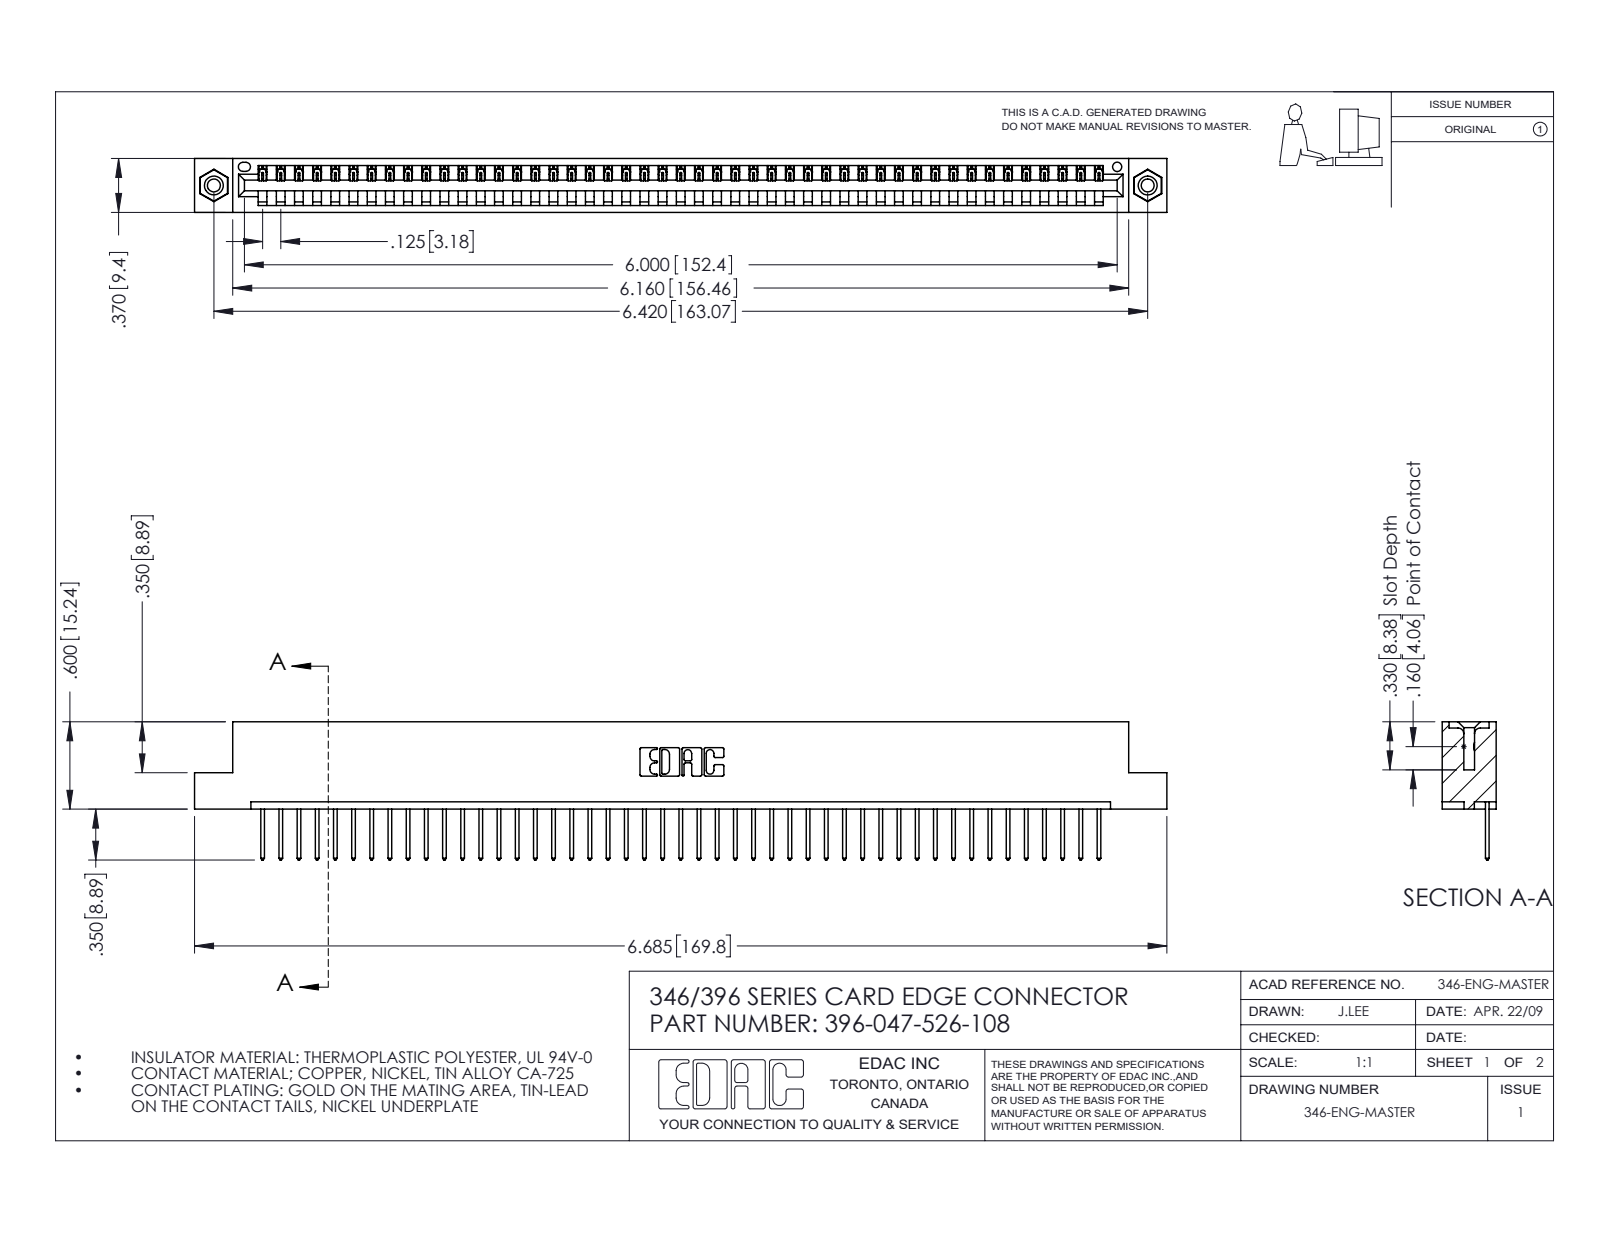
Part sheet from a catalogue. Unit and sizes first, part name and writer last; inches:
Units: inches
Overall size (bounding box): 6.685 × 0.95 × 0.37
Round holes (diameter × count): ⌀0.089 ×2, ⌀0.125 ×2, ⌀0.156 ×2, ⌀0.064 ×1
Round bosses / shafts (diameter × count): ⌀0.155 ×2
Partial cylindrical surfaces — rounded edges, fillets, slot ends (radius × count): R0.006 ×94, R0.01 ×94, R0.01 ×22, R0.007 ×6, R0.031 ×6, R0.026 ×3, R0.031 ×2, R0.04 ×2
Main face-to-face distances: 0.048, 0.322, 0.37, 0.25, 0.072, 0.298, 0.025, 0.148, 0.222, 0.1
Hole centre spacings: 0.246, 6.211, 6.42
Volume: 0.991 in³ · Surface area: 31.52 in²
Bodies: 50 solids, 2908 faces (1988 planar, 904 cylindrical, 16 other)
Part name (STEP PRODUCT): 345-250-001_345-250-003-102; 345-292-001_345-293-126; 396-047-526-108; 346 Part_Flush Mounting Lugs - 0.156 Dia-TI
STEP written by: SolidWorks 2016 (CONFIG_CONTROL_DESIGN)
